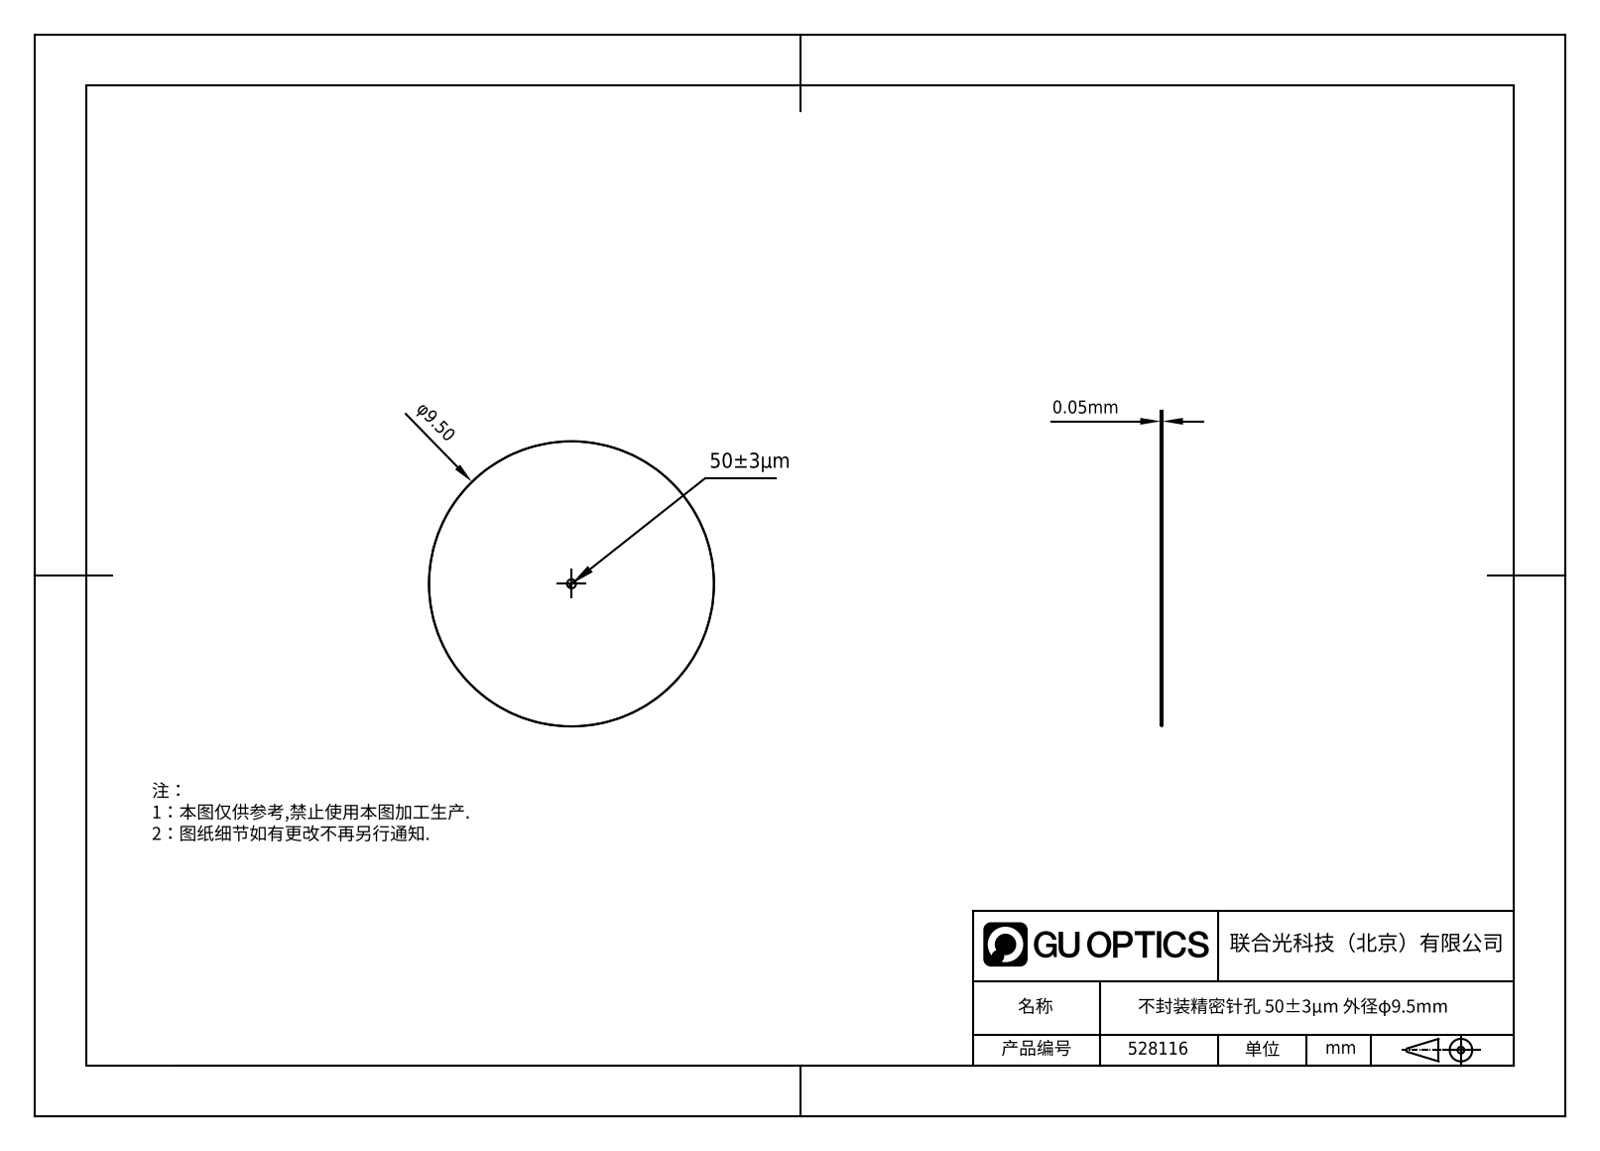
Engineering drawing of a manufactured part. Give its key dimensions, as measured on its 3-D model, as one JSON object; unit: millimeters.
{"part_name": "1.5.3.8-ZXO-9.5-50", "step_written_by": "SolidWorks 2021 (CONFIG_CONTROL_DESIGN)", "units": "millimeters", "bodies": {"solids": 1, "faces": 6, "planar": 2, "cylindrical": 4, "other": 0}, "overall_size": [9.5, 9.5, 0.05], "volume_mm3": 4, "surface_area_mm2": 143, "round_bosses_or_shafts": [[9.5, 1]]}
